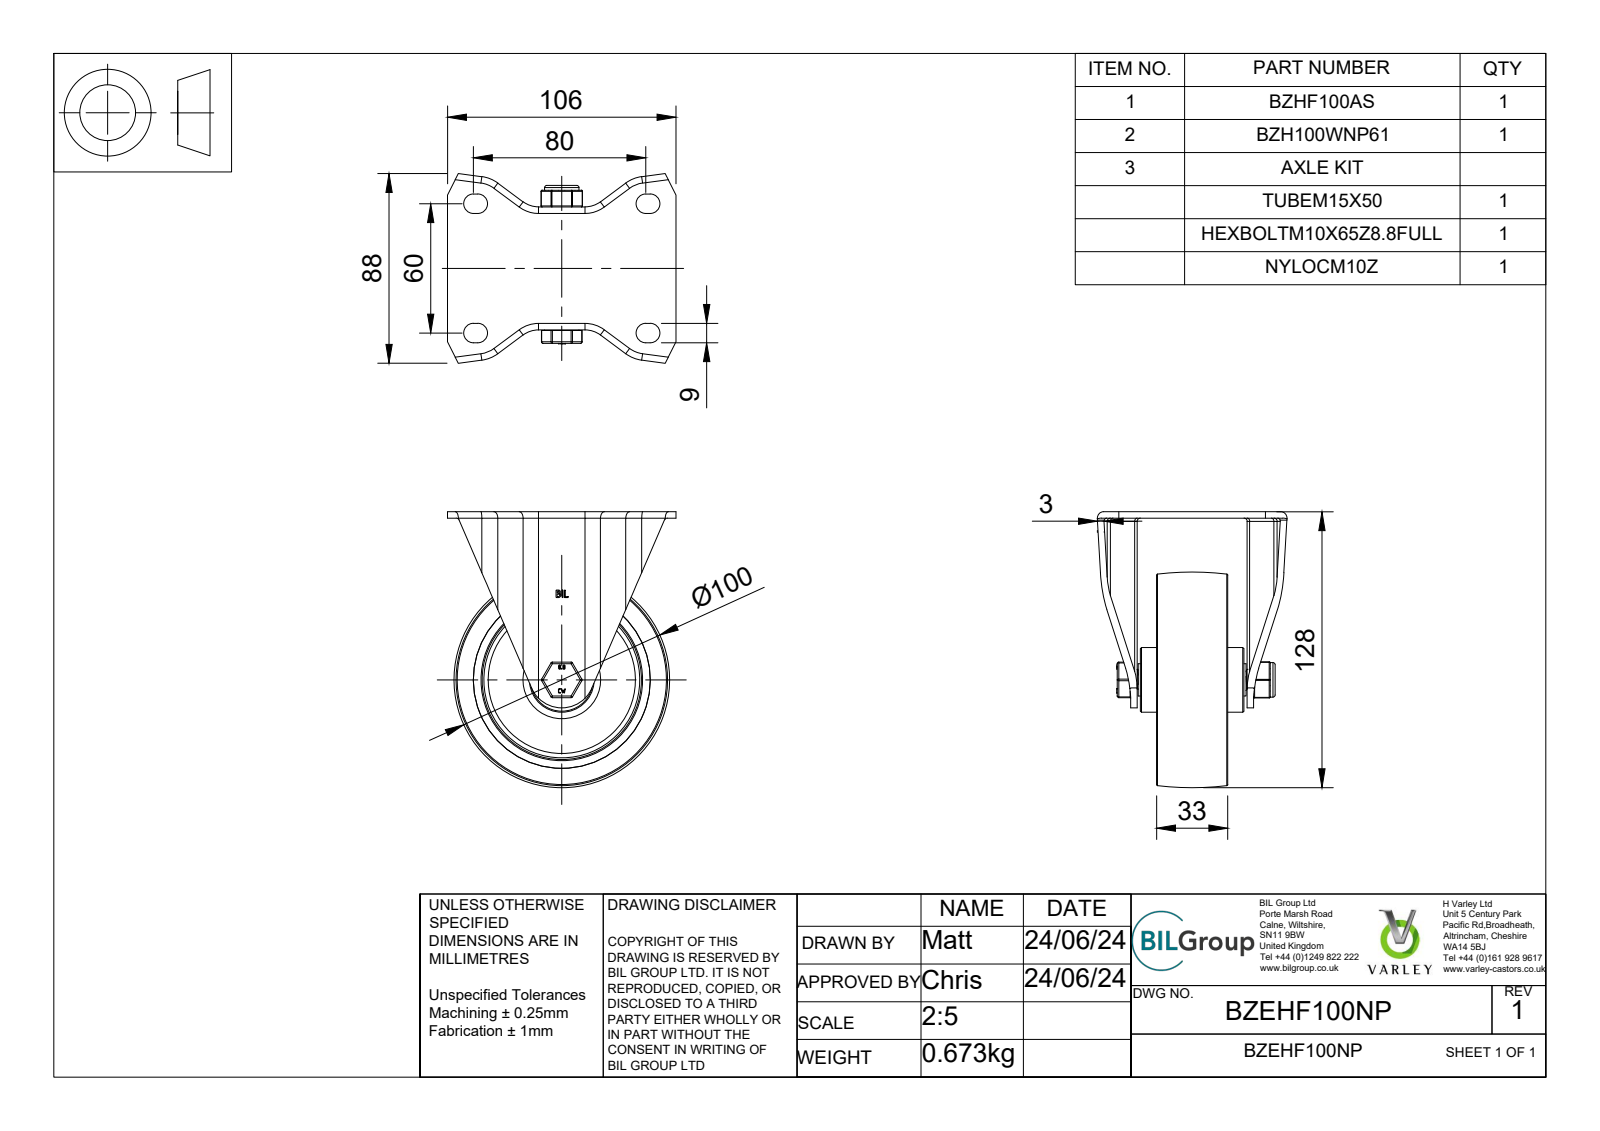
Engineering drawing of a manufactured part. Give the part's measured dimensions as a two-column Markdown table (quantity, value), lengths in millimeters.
| quantity | value |
| --- | --- |
| part name | BZEHF100NP v3; BZHF100AS v1; ZINC PLATED, PRESSED STEEL BRACKET; BZH100WNP61 v1 (+8 more) |
| STEP written by | Autodesk Translation Framework v13.14.0.145 (AUTOMOTIVE_DESIGN) |
| units | millimeters |
| bodies | 7 solids, 421 faces (137 planar, 182 cylindrical, 102 other) |
| overall size | 128 × 106 × 88 |
| volume | 226 830 mm³ |
| surface area | 101 378 mm² |
| round holes (diameter × count) | 10 × 1, 10.25 × 1, 10.5 × 1, 12 × 1, 15.4 × 1, 82 × 1 |
| round bosses / shafts (diameter × count) | 30 × 1, 16 × 1, 15 × 1, 9.85 × 1, 8.14 × 1 |
| partial cylindrical surfaces (radius × count) | 0.5 × 18, 0.75 × 12, 1.5 × 12, 3 × 10, 4.5 × 8, 6 × 4, 8 × 4, 12 × 4 |
| main face-to-face distances | 3, 19, 14, 9, 23, 28, 42, 12, 54, 26 |
